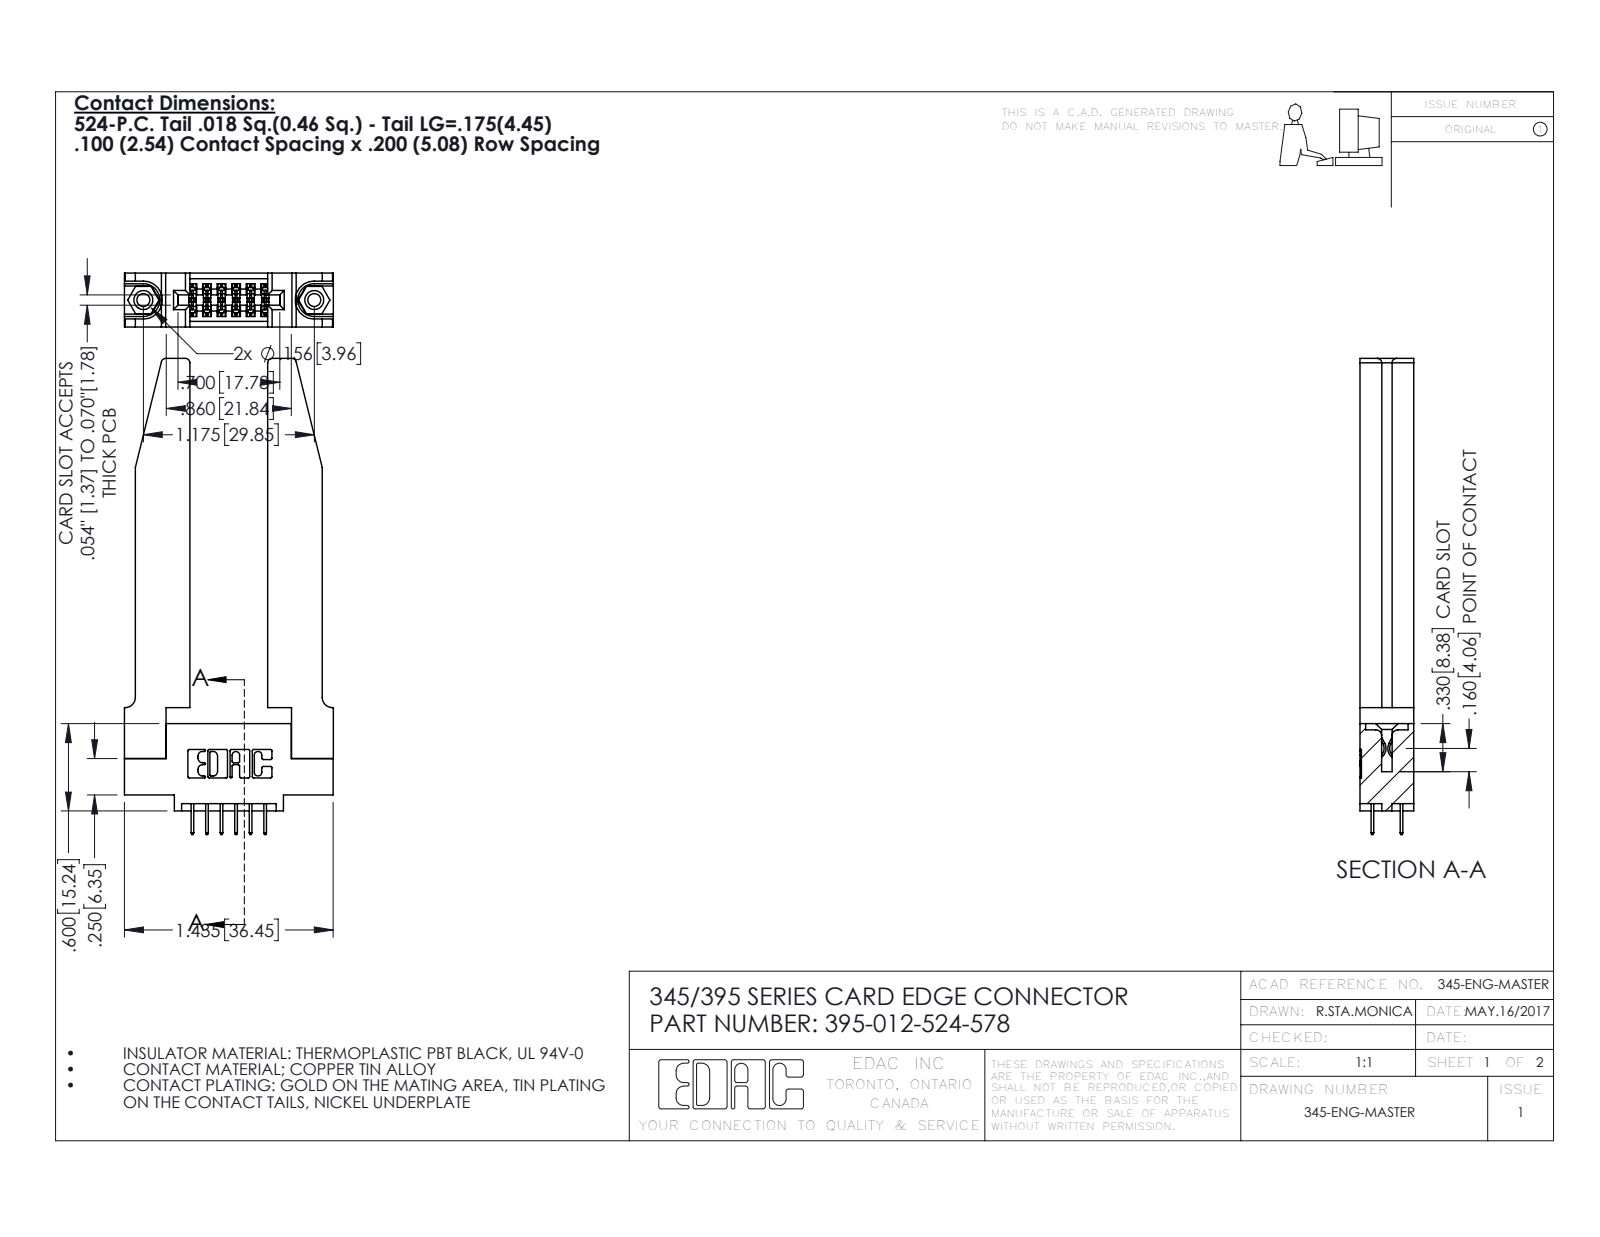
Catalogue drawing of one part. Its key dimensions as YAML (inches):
part_name: "345-292-001_345-293-124; 345 Part_0.110 Offset - 0.156 Dia-TH; 345-220-078_345-220-078; 395-012-524-578 (+1 more)"
step_written_by: "SolidWorks 2016 (CONFIG_CONTROL_DESIGN)"
units: inches
bodies: {solids: 17, faces: 1012, planar: 694, cylindrical: 266, other: 52}
overall_size: [3.272, 1.436, 0.37]
volume: 0.664
surface_area: 16.73
round_holes:
  - {diameter: 0.089, count: 2}
  - {diameter: 0.125, count: 2}
  - {diameter: 0.156, count: 2}
  - {diameter: 0.064, count: 1}
round_bosses_or_shafts:
  - {diameter: 0.155, count: 2}
partial_cylinders:
  - {radius: 0.01, count: 22}
  - {radius: 0.006, count: 18}
  - {radius: 0.03, count: 8}
  - {radius: 0.007, count: 6}
  - {radius: 0.031, count: 6}
  - {radius: 0.026, count: 3}
  - {radius: 0.014, count: 2}
  - {radius: 0.019, count: 2}
face_to_face_distances: [0.37, 0.15, 0.22, 0.535, 0.072, 0.148, 0.298, 0.077, 0.071, 0.055]
hole_center_spacings: [0.27, 0.946, 1.175]
